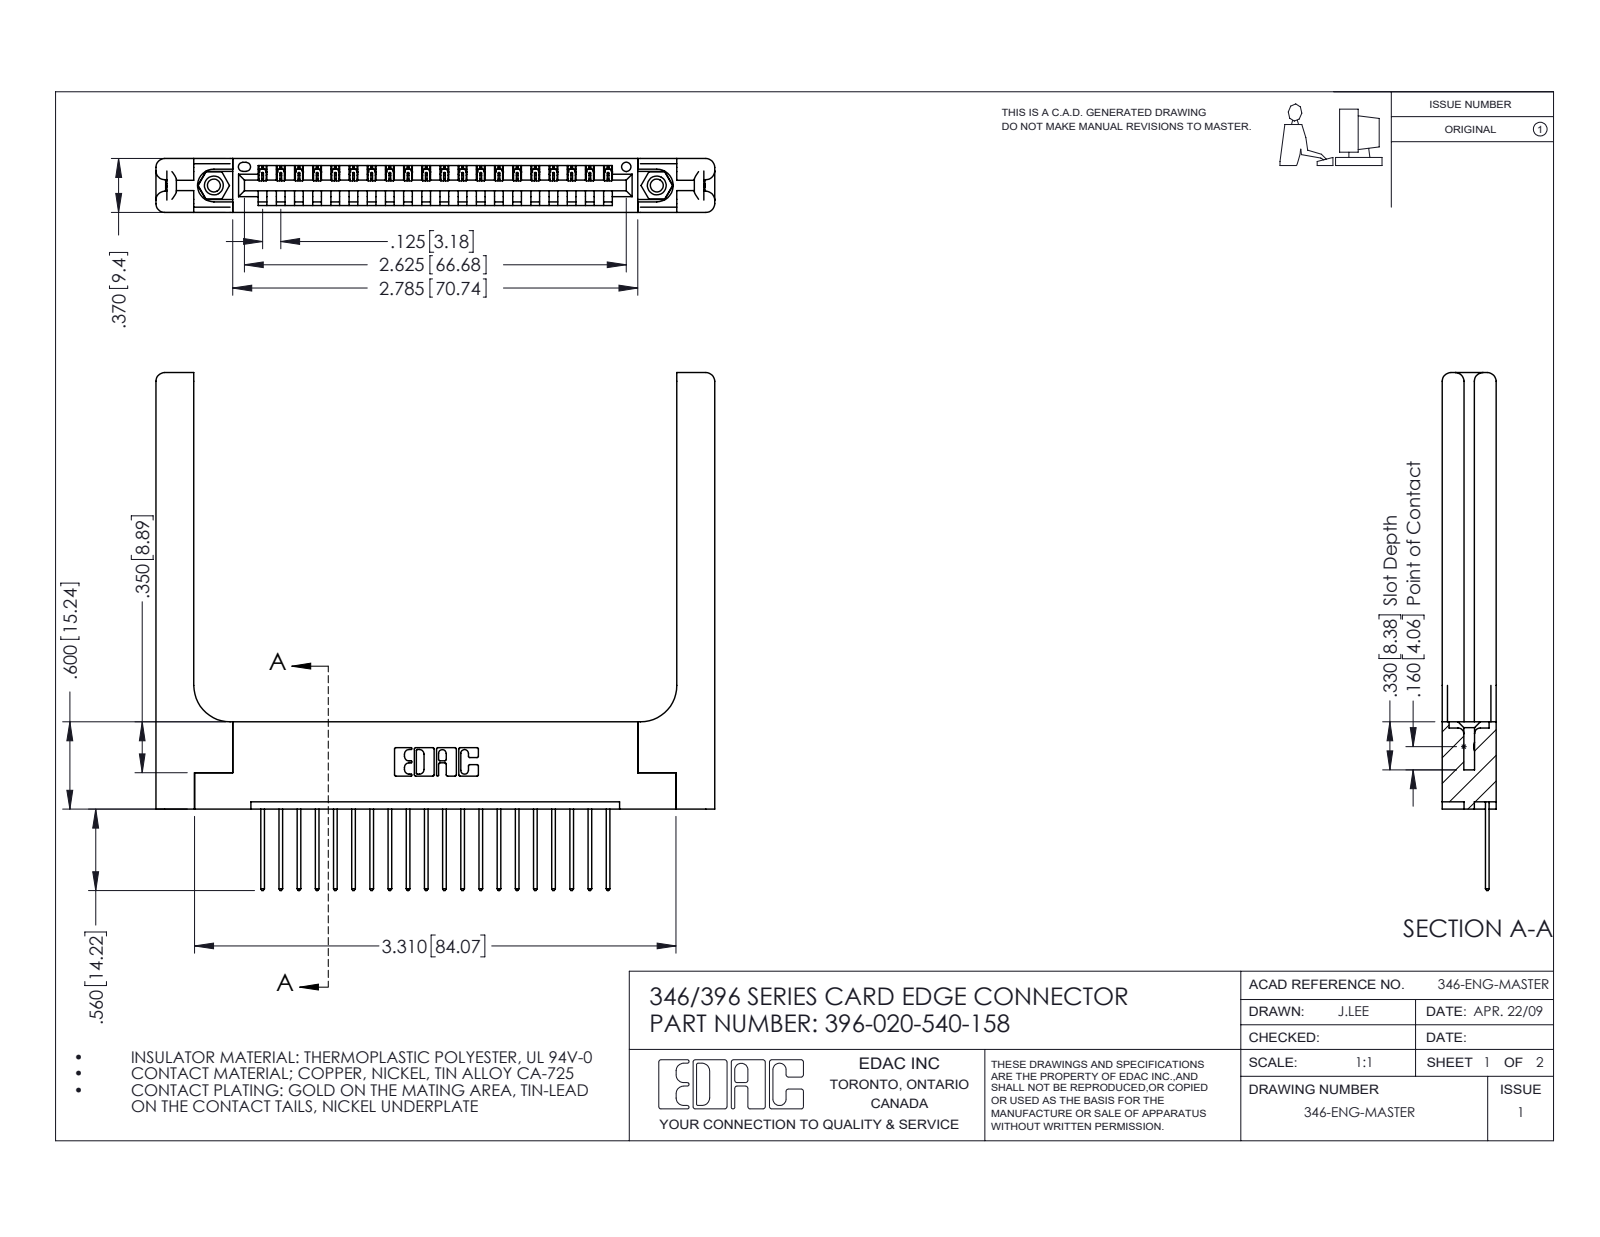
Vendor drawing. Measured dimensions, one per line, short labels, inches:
name: 396-020-540-158; 345-292-001_345-293-140; 346-220-058_345-220-058; 345-250-001_345-250-001-102 (+1 more)
written by: SolidWorks 2016 (CONFIG_CONTROL_DESIGN)
unit: in
bodies: 25 solids, 1538 faces (1024 planar, 454 cylindrical, 60 other)
size: 3.841 × 3.56 × 0.37
volume: 1.021 in³; area: 25.8 in²
holes: 2× ⌀0.089, 2× ⌀0.125, 2× ⌀0.156, 1× ⌀0.064
bosses: 2× ⌀0.155
rounds: 40× R0.006, 40× R0.01, 22× R0.01, 16× R0.06, 6× R0.007, 6× R0.031, 3× R0.026, 2× R0.03
face distances: 0.37, 0.072, 0.048, 0.322, 0.15, 0.148, 0.25, 0.298, 0.025, 0.102
hole spacings: 0.246, 2.837, 3.045
